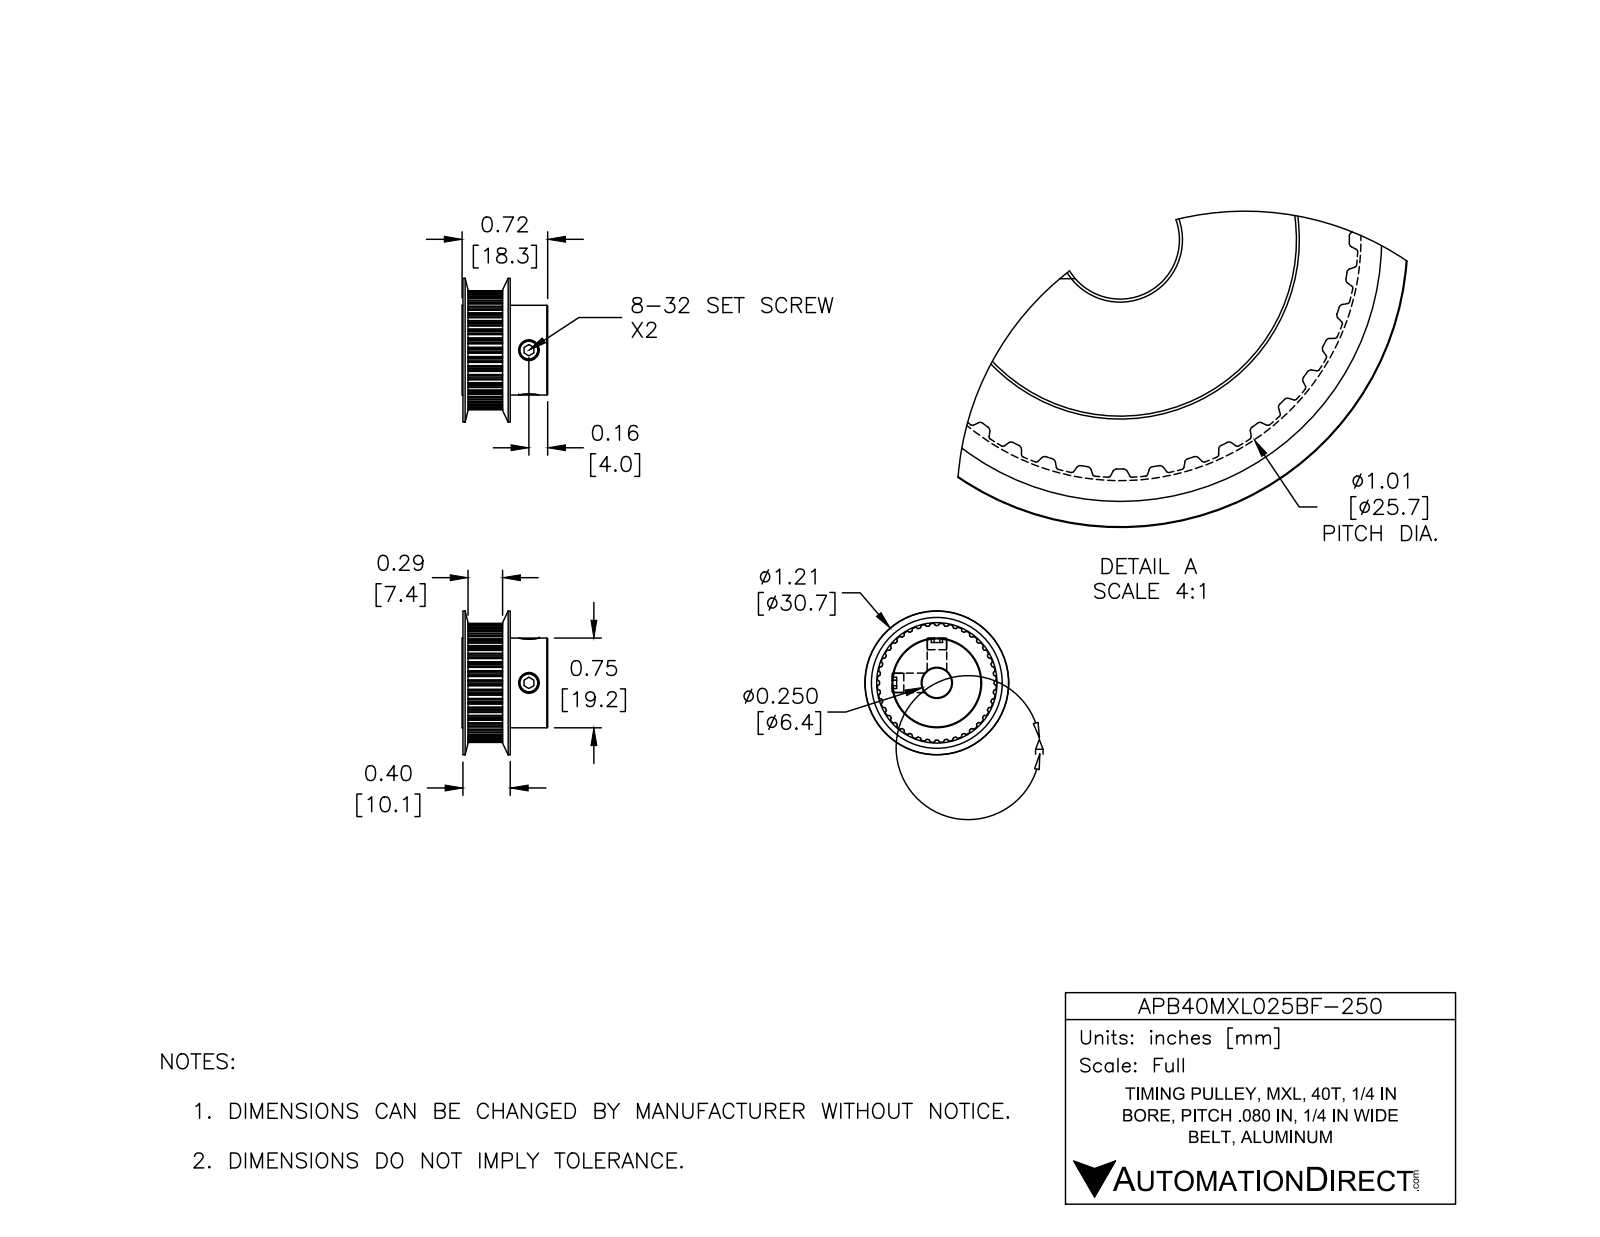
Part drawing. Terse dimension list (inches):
name: APB40MXL025BF-250
written by: SolidWorks 2016 (AUTOMOTIVE_DESIGN)
unit: in
bodies: 3 solids, 413 faces (104 planar, 283 cylindrical, 26 other)
size: 1.21 × 1.21 × 0.719
volume: 0.411 in³; area: 6.062 in²
holes: 2× ⌀0.164, 1× ⌀0.25
bosses: 2× ⌀0.16, 1× ⌀0.754
rounds: 80× R0.005, 80× R0.009, 1× R0.482, 1× R0.5
face distances: 0.362, 0.025, 0.387, 0.719, 0.694, 0.332, 0.431, 0.43, 0.05, 0.025
